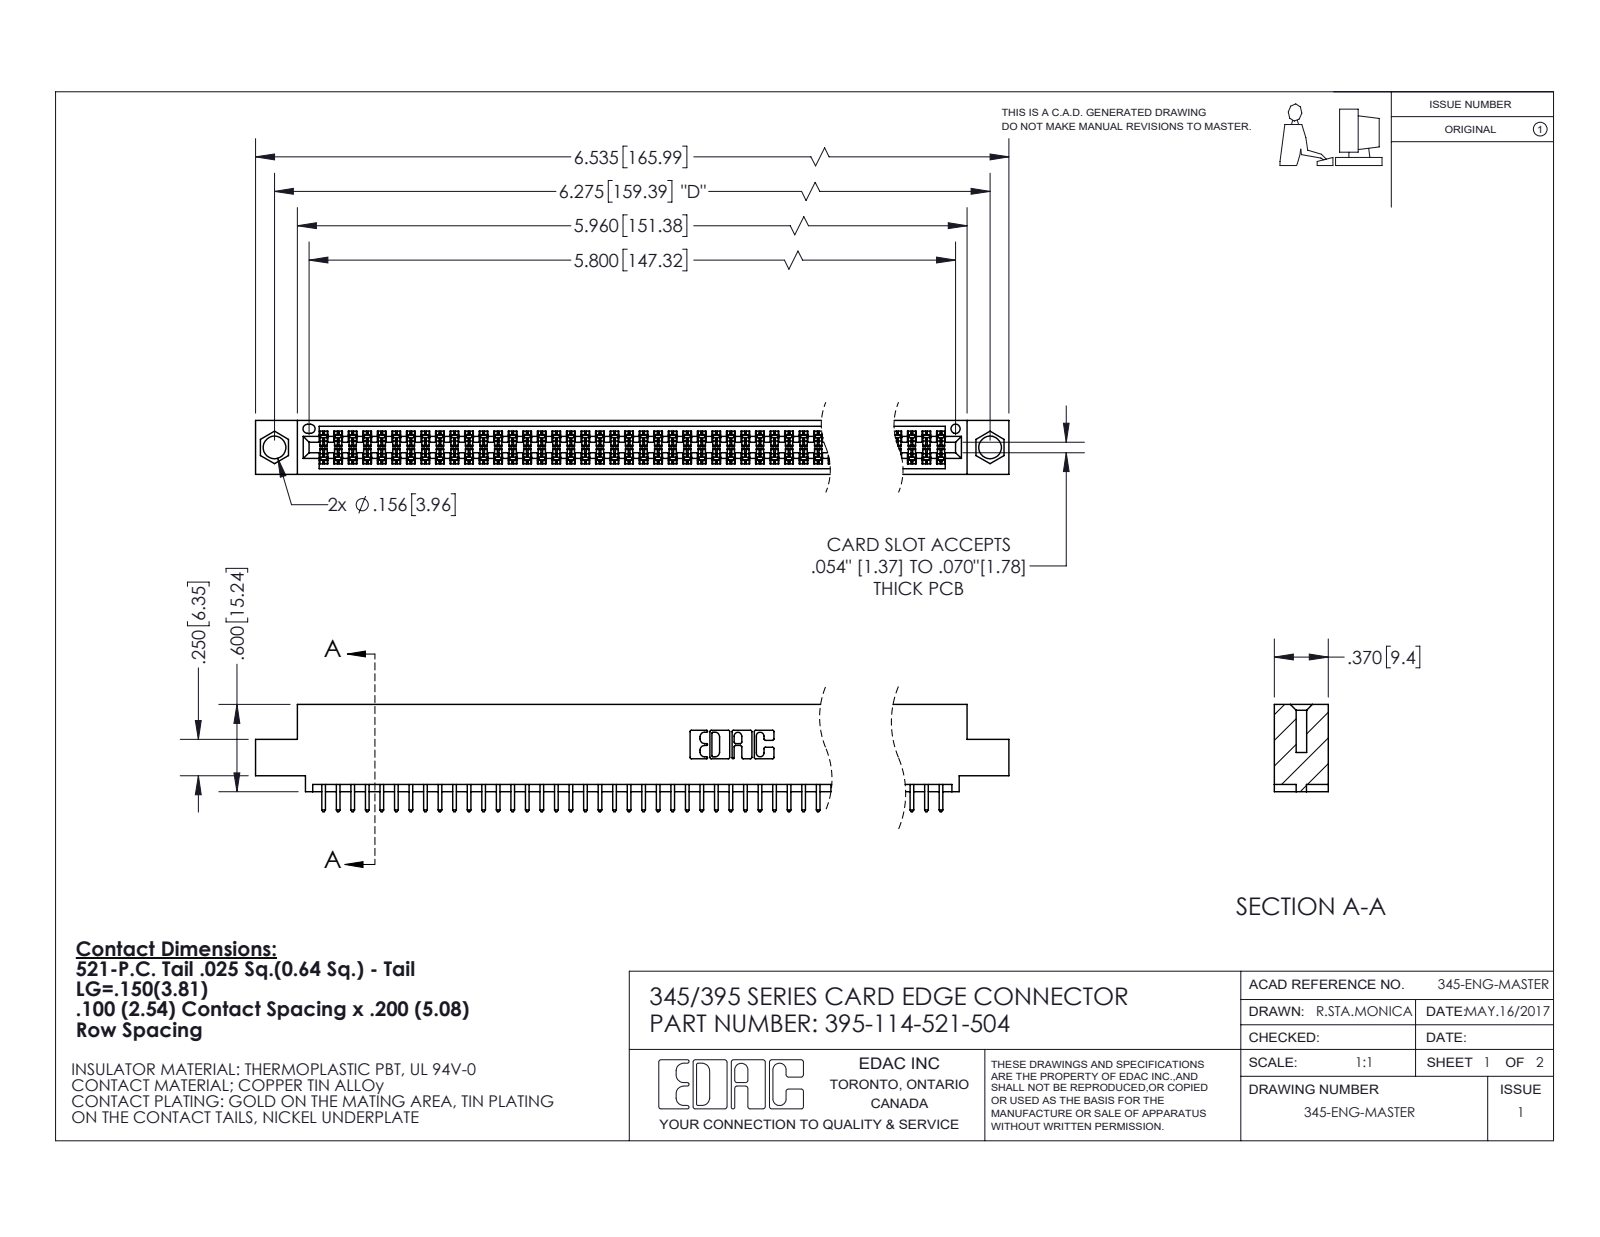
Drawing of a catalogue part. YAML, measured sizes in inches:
part_name: "345-292-001_345-293-121; 395-114-521-504; 345 Part_0.110 Offset - 0.156 Dia-TI"
step_written_by: "SolidWorks 2020 (CONFIG_CONTROL_DESIGN)"
units: inches
bodies: {solids: 115, faces: 5844, planar: 3860, cylindrical: 1984, other: 0}
overall_size: [6.535, 0.737, 0.37]
volume: 0.979
surface_area: 36.64
round_holes:
  - {diameter: 0.156, count: 2}
  - {diameter: 0.064, count: 1}
partial_cylinders:
  - {radius: 0.006, count: 171}
  - {radius: 0.01, count: 114}
  - {radius: 0.01, count: 22}
  - {radius: 0.007, count: 6}
  - {radius: 0.031, count: 6}
  - {radius: 0.026, count: 3}
  - {radius: 0.014, count: 2}
  - {radius: 0.019, count: 2}
face_to_face_distances: [0.298, 0.072, 0.2, 0.098, 0.272, 0.025, 0.37, 0.225, 0.175, 0.149]
hole_center_spacings: [0.27, 6.039, 6.275]
